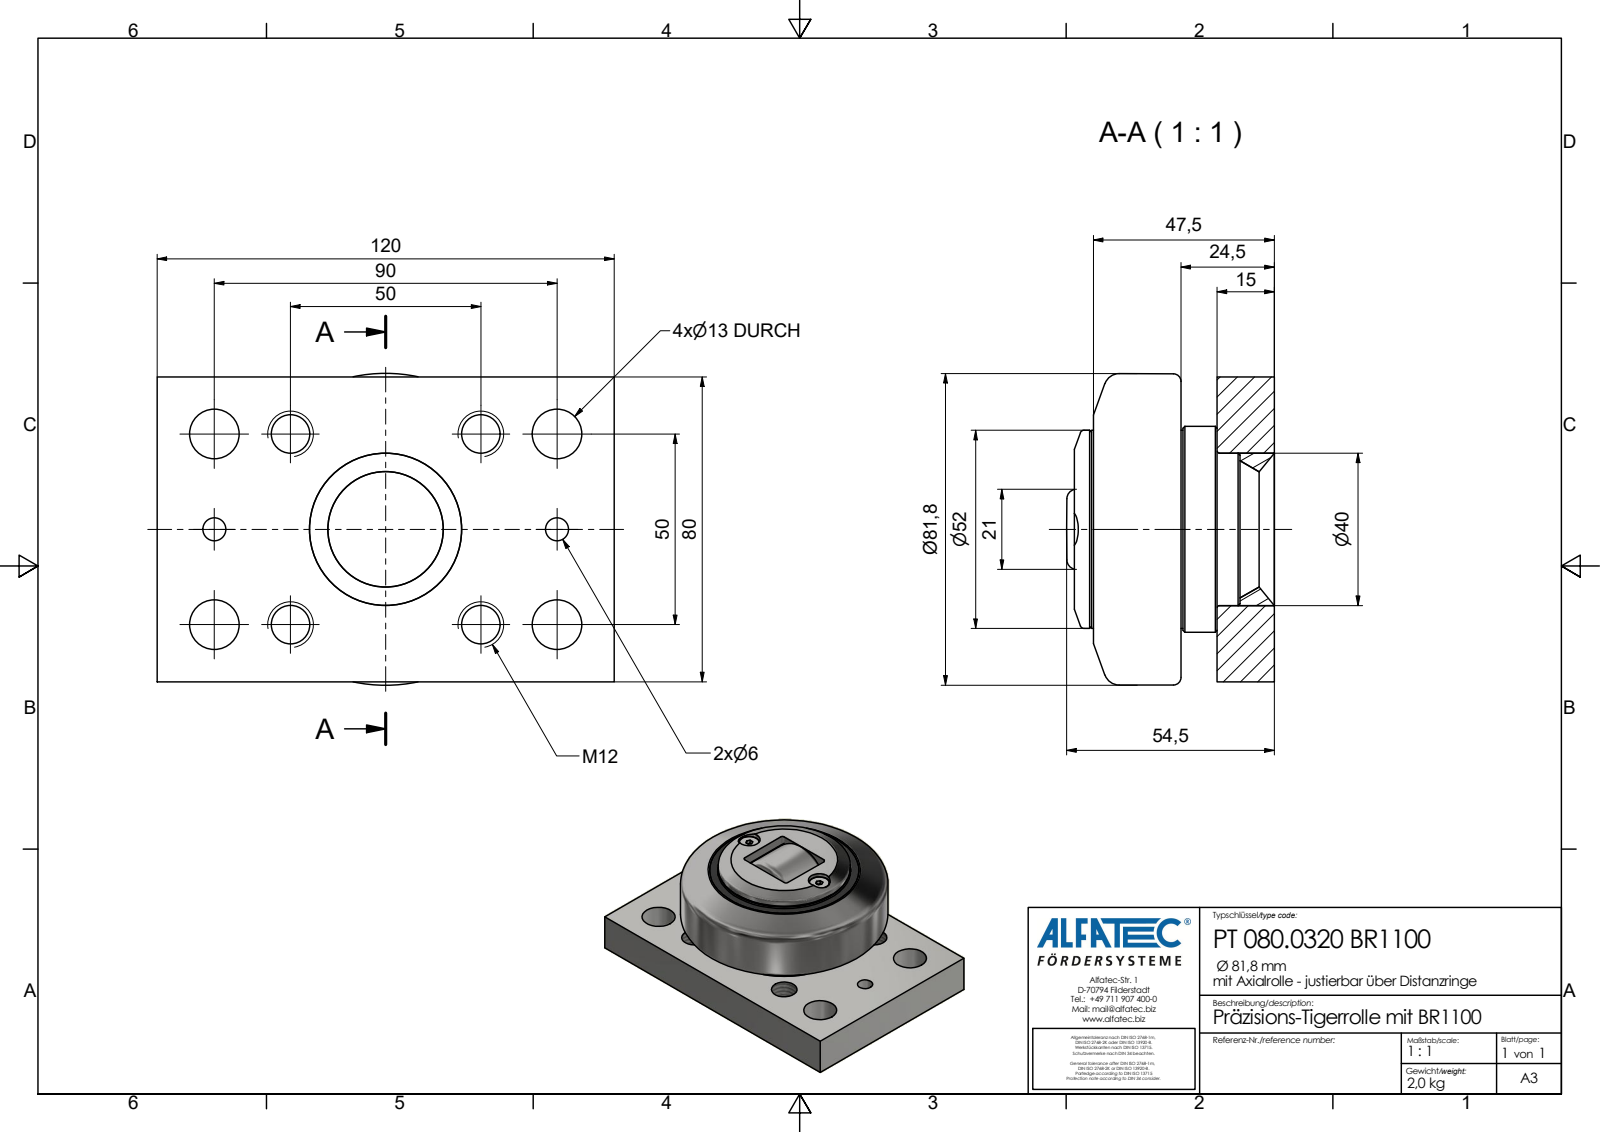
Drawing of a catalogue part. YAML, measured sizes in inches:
part_name: "PT 080.0320 BR1100_Kontur"
step_written_by: "Autodesk Inventor 2020 (AP242_MANAGED_MODEL_BASED_3D_ENGINEERING_MIM_LF)"
units: inches
bodies: {solids: 1, faces: 104, planar: 46, cylindrical: 37, other: 21}
overall_size: [4.724, 3.22, 2.146]
volume: 16.62
surface_area: 68.98
round_holes:
  - {diameter: 0.398, count: 4}
  - {diameter: 0.512, count: 4}
  - {diameter: 0.177, count: 2}
  - {diameter: 0.236, count: 2}
  - {diameter: 0.339, count: 2}
  - {diameter: 1.819, count: 1}
round_bosses_or_shafts:
  - {diameter: 0.307, count: 2}
  - {diameter: 0.157, count: 2}
  - {diameter: 2.126, count: 1}
  - {diameter: 2.047, count: 1}
  - {diameter: 1.291, count: 1}
partial_cylinders:
  - {radius: 0.039, count: 4}
  - {radius: 0.315, count: 1}
  - {radius: 0.354, count: 1}
  - {radius: 0.413, count: 1}
face_to_face_distances: [0.591, 0.965, 0.374, 3.15, 4.724, 1.89, 0.02, 0.925, 1.87, 1.28]
hole_center_spacings: [1.969, 0.787, 0.984, 1.008, 1.261, 1.392, 1.406, 2.009]
